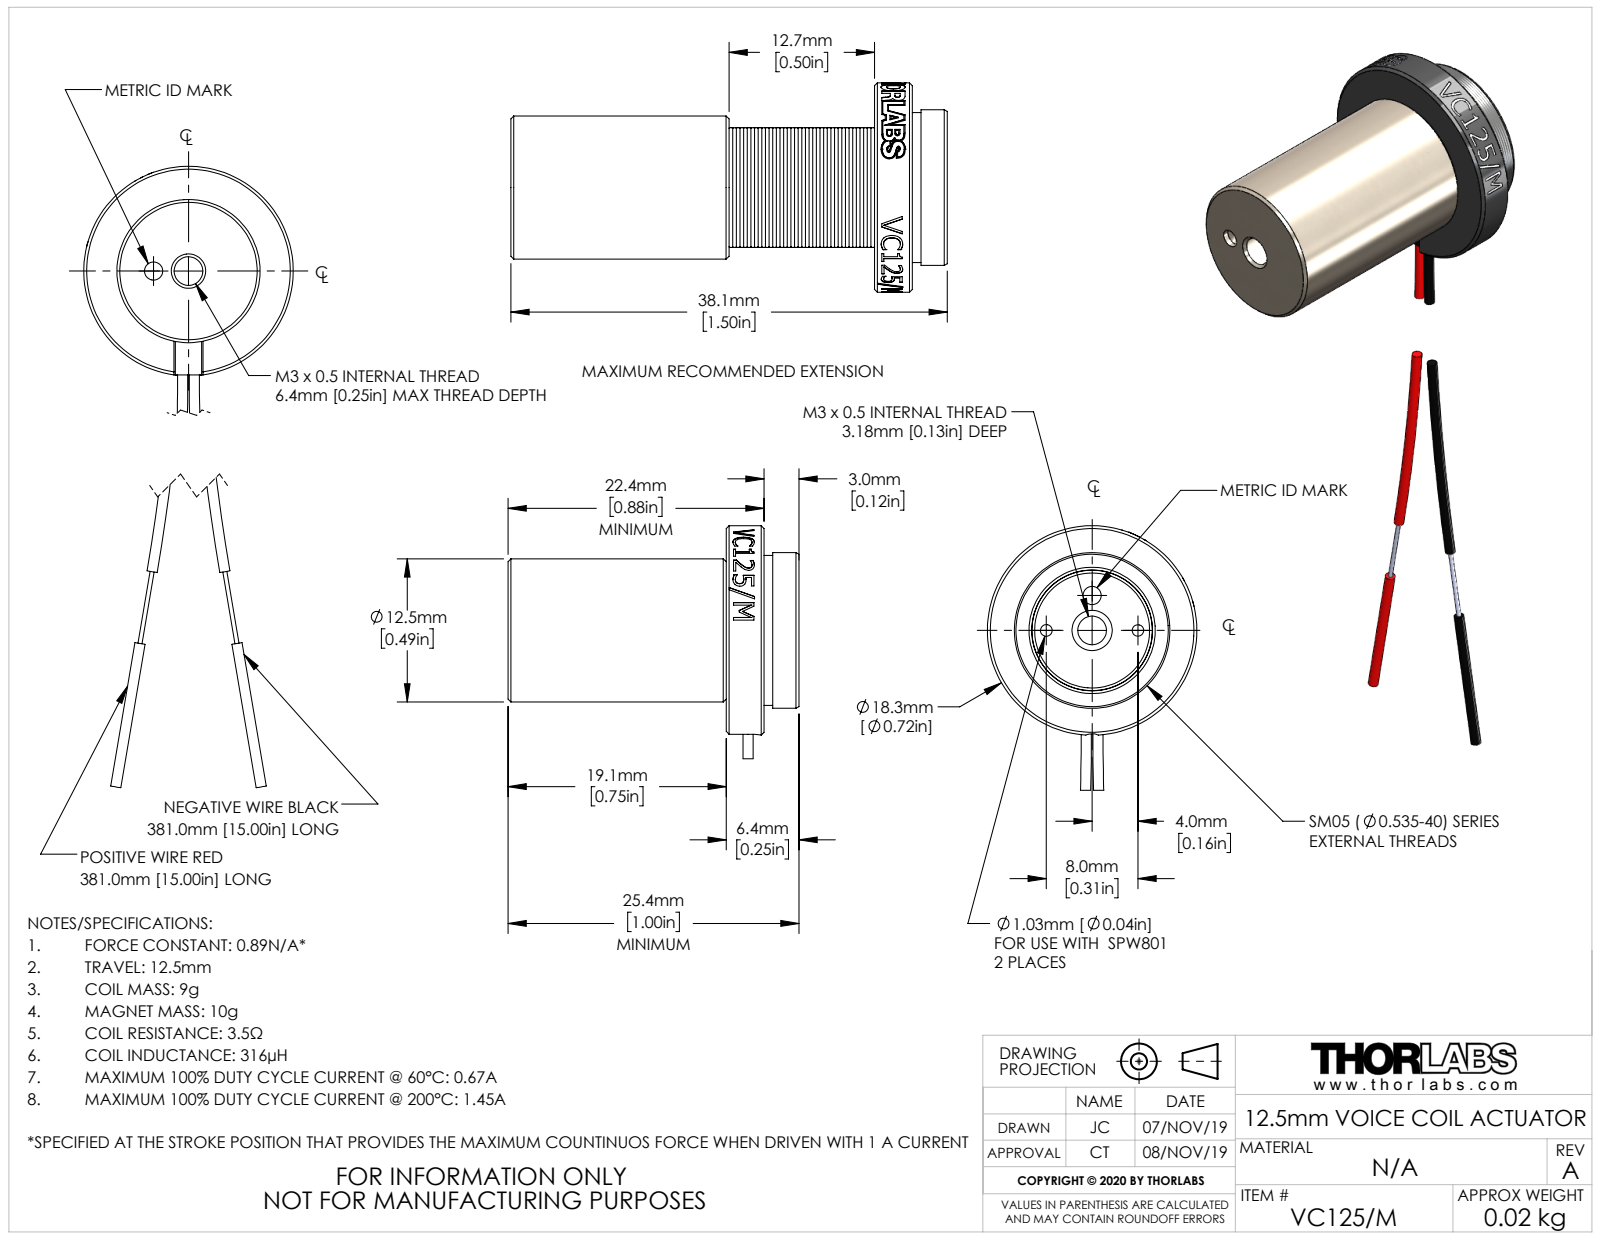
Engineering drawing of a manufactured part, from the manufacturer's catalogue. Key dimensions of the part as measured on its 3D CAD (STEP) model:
Part name (STEP PRODUCT): TTN215763-E0W
STEP written by: SolidWorks 2018 (AUTOMOTIVE_DESIGN)
Units: inches
Bodies: 5 solids, 650 faces (136 planar, 160 cylindrical, 354 other)
Overall size (bounding box): 1 × 0.72 × 0.719
Volume: 0.189 in³ · Surface area: 6.792 in²
Round holes (diameter × count): ⌀0.063 ×2, ⌀0.04 ×1, ⌀0.04 ×1, ⌀0.118 ×1, ⌀0.27 ×1, ⌀0.414 ×1, ⌀0.42 ×1, ⌀0.437 ×1
Round bosses / shafts (diameter × count): ⌀0.72 ×1, ⌀0.535 ×1, ⌀0.515 ×1, ⌀0.492 ×1, ⌀0.415 ×1, ⌀0.412 ×1, ⌀0.25 ×1
Partial cylindrical surfaces — rounded edges, fillets, slot ends (radius × count): R0.05 ×1, R0.359 ×1
Main face-to-face distances: 0.13, 0.75, 0.755, 0.625, 0.12, 0.25, 0.875, 1, 0.88, 0.125
Hole centre spacings: 0.12, 0.157, 0.198, 0.037, 0.17, 0.278, 0.315
